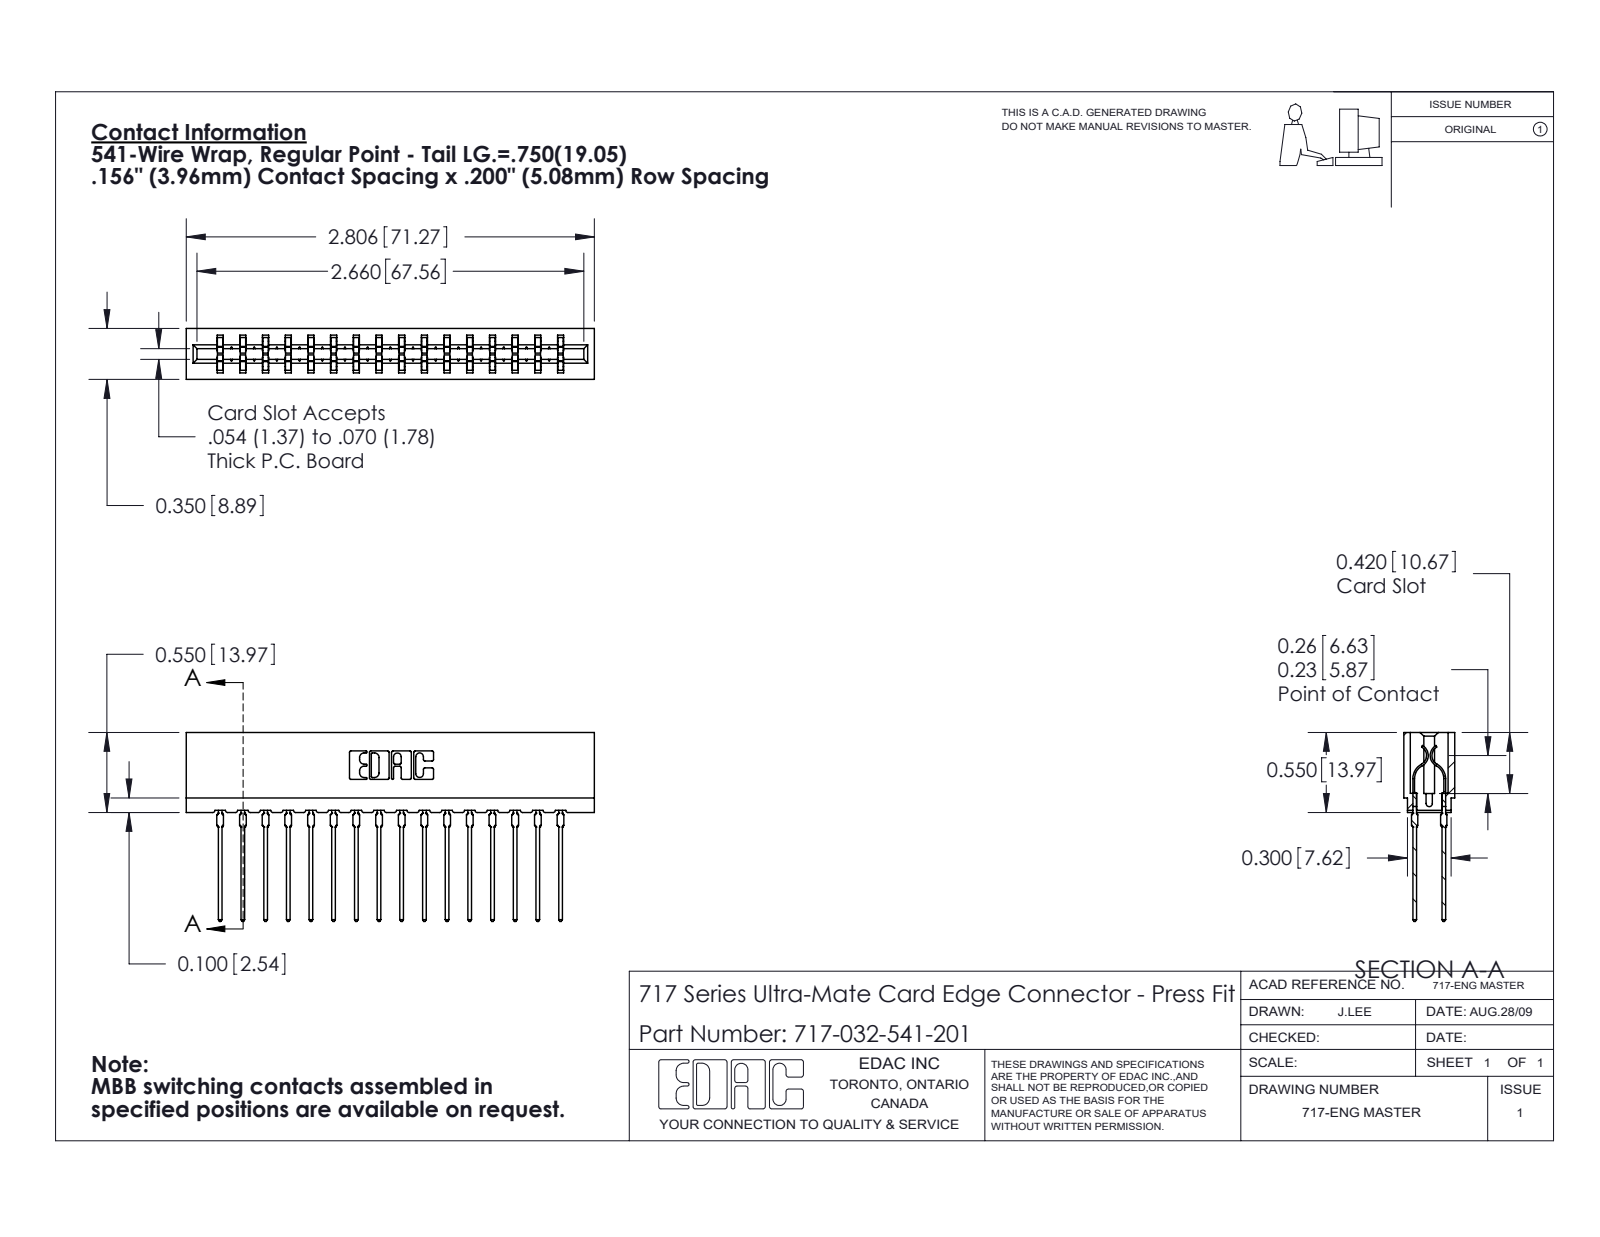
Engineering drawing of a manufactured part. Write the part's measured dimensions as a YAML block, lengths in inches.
part_name: "717 Part_Insulator Option - 06; 717-032-541-201; 745-292-001_541"
step_written_by: "SolidWorks 2020 (CONFIG_CONTROL_DESIGN)"
units: inches
bodies: {solids: 33, faces: 2974, planar: 1542, cylindrical: 600, other: 832}
overall_size: [2.806, 1.299, 0.35]
volume: 0.393
surface_area: 15.83
partial_cylinders:
  - {radius: 0.021, count: 64}
  - {radius: 0.015, count: 32}
  - {radius: 0.01, count: 22}
  - {radius: 0.005, count: 8}
  - {radius: 0.011, count: 8}
  - {radius: 0.007, count: 6}
  - {radius: 0.031, count: 6}
  - {radius: 0.026, count: 3}
face_to_face_distances: [0.212, 0.138, 0.35, 0.063, 0.287, 0.076, 0.149, 0.156, 0.468, 0.624]
